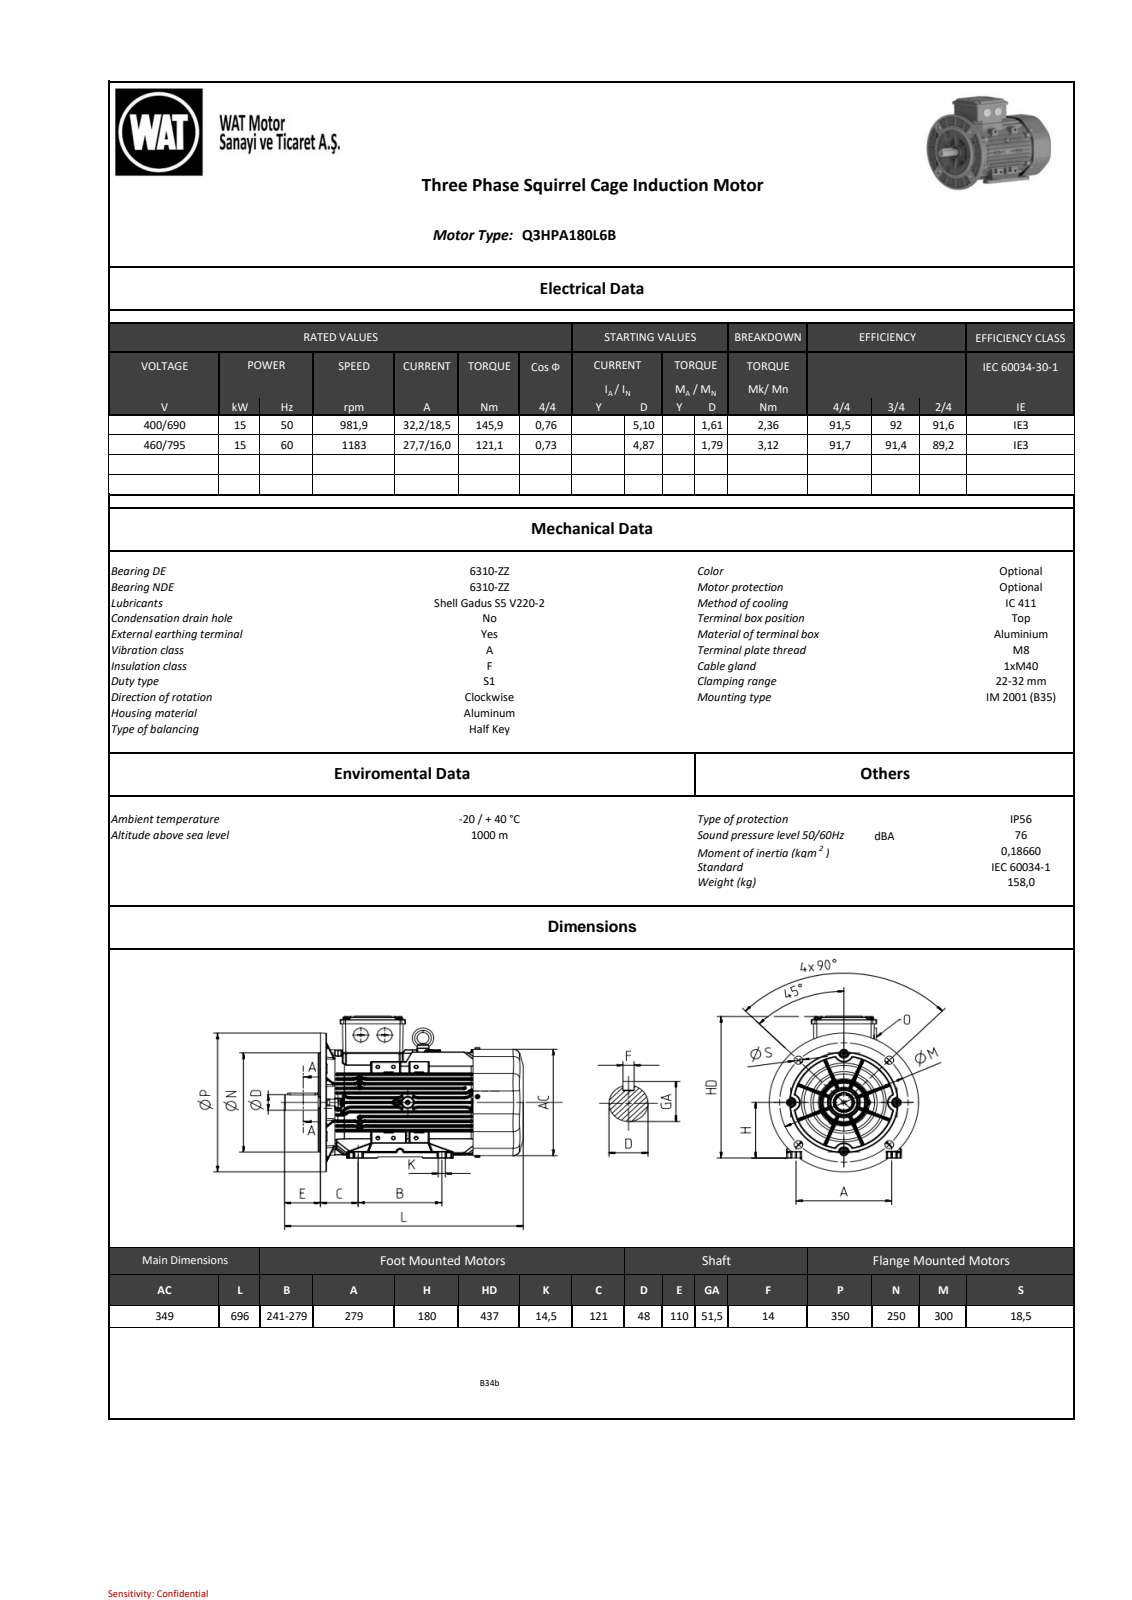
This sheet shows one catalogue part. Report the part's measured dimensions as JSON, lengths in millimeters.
{"part_name": "001_objects", "step_written_by": "SIEMENS PLM Software NX2206.8101 (AP203_CONFIGURATION_CONTROLLED_3D_DESIGN_OF_MECHANICAL_PARTS_AND_ASSEMBLIES_MIM_LF)", "units": "millimeters", "bodies": {"solids": 0, "faces": 6588, "planar": 2043, "cylindrical": 2408, "other": 2137}, "overall_size": [696, 432, 357.1], "round_holes": [[19, 4], [22, 2], [25.05, 2], [8, 1], [80, 1], [82, 1], [240, 1]], "round_bosses_or_shafts": [[18.1, 4], [16, 4], [12, 4], [9.5, 4], [8, 4], [13, 3], [55, 2], [51.2, 2]], "partial_cylinders_radius": [[2, 742], [1, 593], [3, 93], [5, 56], [8, 22], [0.5, 19], [1, 18], [4, 16]], "face_to_face_distances": [1.2, 16.21, 5, 32.48, 16.27, 171.05, 141.35, 157.62, 173.83, 157.07], "hole_center_spacings": [150.01, 212.14, 300.01, 52, 91, 137.03, 149.83, 149.84]}
